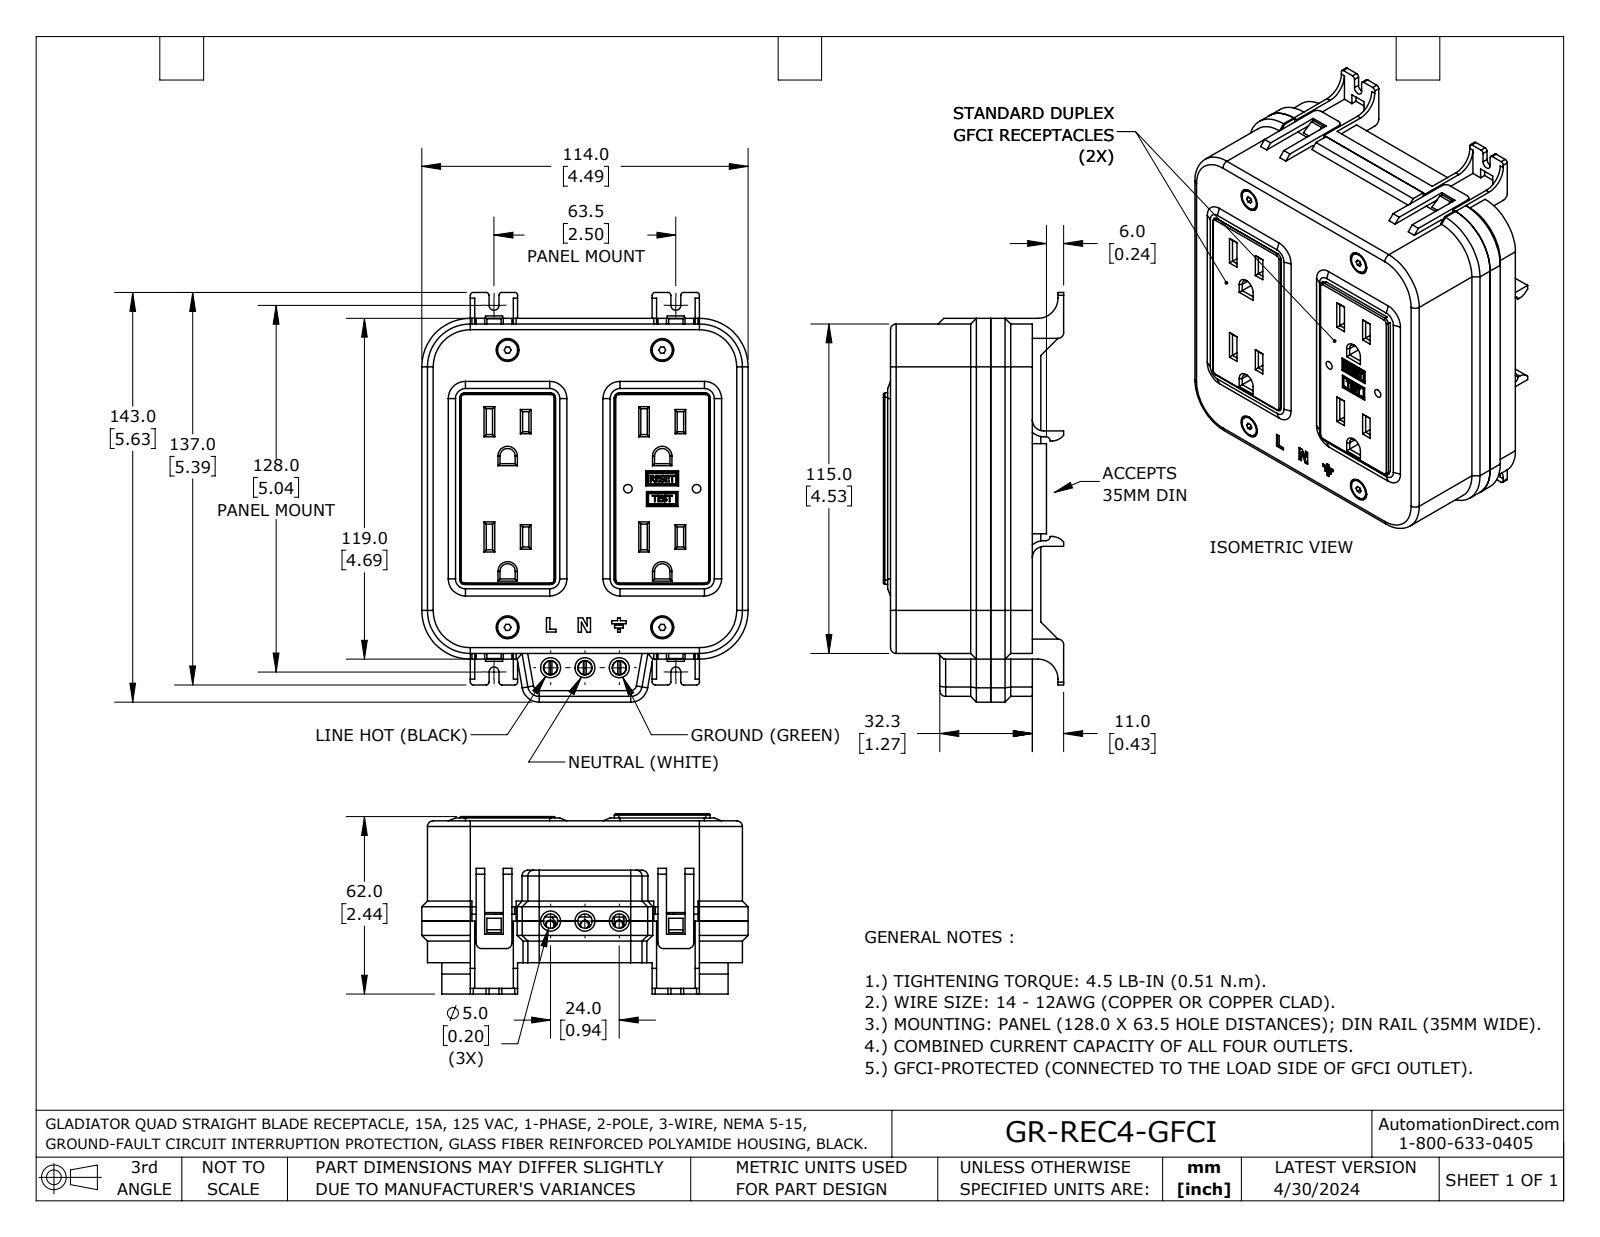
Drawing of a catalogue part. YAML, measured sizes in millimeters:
part_name: "GR-REC4-GFCI"
step_written_by: "SolidWorks 2023 (AUTOMOTIVE_DESIGN)"
units: millimeters
bodies: {solids: 24, faces: 2273, planar: 1654, cylindrical: 377, other: 242}
overall_size: [143, 114, 63]
volume: 275300
surface_area: 161300
round_holes:
  - {diameter: 3, count: 18}
  - {diameter: 5, count: 9}
  - {diameter: 4.5, count: 8}
  - {diameter: 2.8, count: 4}
  - {diameter: 3.5, count: 4}
  - {diameter: 8, count: 4}
  - {diameter: 3.9, count: 2}
round_bosses_or_shafts:
  - {diameter: 3.3, count: 16}
  - {diameter: 7, count: 13}
  - {diameter: 2.8, count: 10}
  - {diameter: 7.5, count: 8}
  - {diameter: 4.8, count: 6}
  - {diameter: 8, count: 3}
  - {diameter: 3.3, count: 2}
  - {diameter: 5, count: 1}
partial_cylinders:
  - {radius: 2, count: 60}
  - {radius: 1, count: 33}
  - {radius: 1.5, count: 18}
  - {radius: 1.8, count: 12}
  - {radius: 0.5, count: 10}
  - {radius: 3, count: 10}
  - {radius: 0.8, count: 8}
  - {radius: 4, count: 6}
face_to_face_distances: [2, 47.5, 3.5, 1, 6, 35, 2.8, 1.5, 49.5, 108]
hole_center_spacings: [12.1, 96.1, 8, 12, 24, 28, 54, 20]
